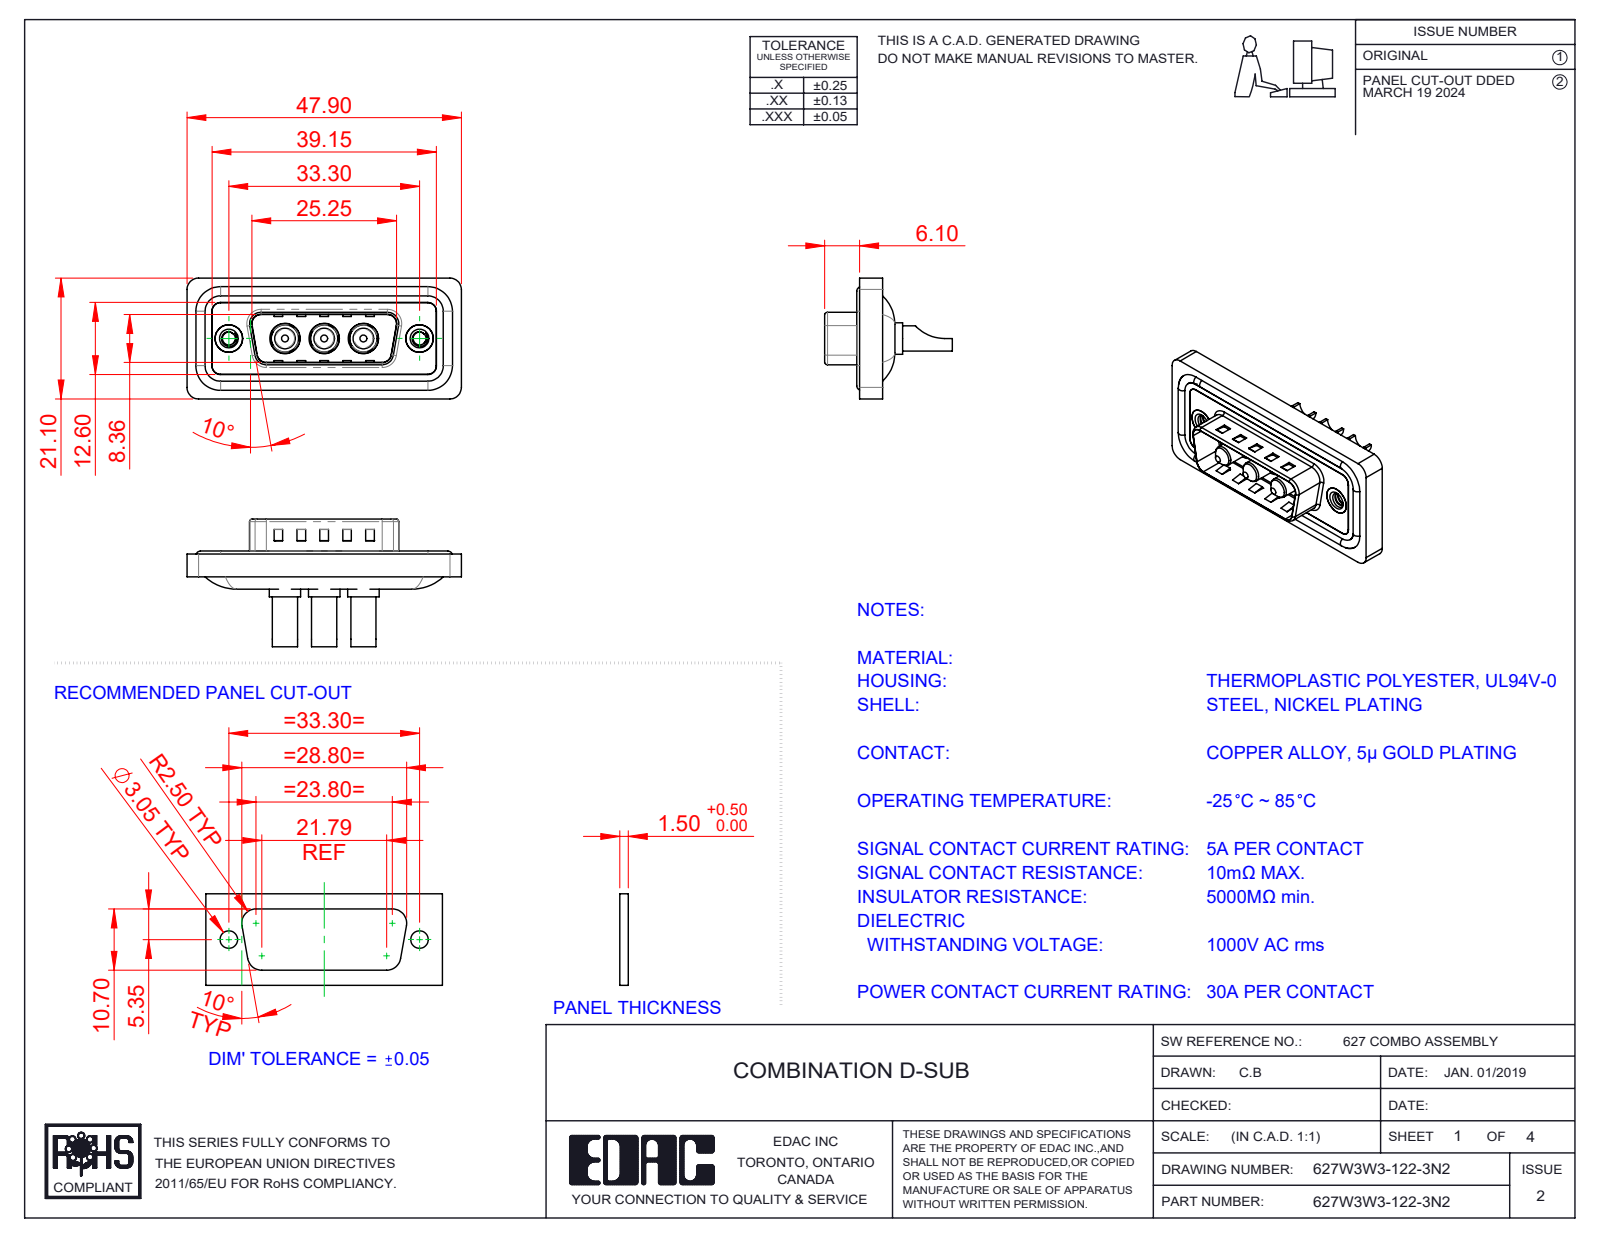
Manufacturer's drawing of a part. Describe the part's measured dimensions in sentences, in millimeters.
The part is named "627Combo Waterproof Housing_15 Contacts; Power Pin_30A SC; 627W3W3-122-3N2; 627Combo Shell Rear_15 Contacts (+3 more)". Its 3-D file was written by "SolidWorks 2023 (CONFIG_CONTROL_DESIGN)". It is 13 solids with 582 faces: 216 planar, 250 cylindrical and 116 other. Overall it measures 47.9 by 22.3 by 21.1 millimeters. Its volume is 5 658 cubic millimeters and its surface area 9 076 square millimeters. Round holes: 3 of diameter 3.5, 3 of diameter 4.85, 3 of diameter 5.3, 2 of diameter 2.26, 2 of diameter 4, 2 of diameter 4.8, 2 of diameter 5. Round bosses or shafts: 4 of diameter 1.6, 3 of diameter 5.5, 3 of diameter 5.2, 3 of diameter 4.75, 3 of diameter 4.4, 3 of diameter 3.75, 3 of diameter 3.6, 2 of diameter 4.9. Partial cylindrical surfaces (rounded edges, fillets, slot ends): 26 of radius 1.5, 20 of radius 2, 8 of radius 0.5, 8 of radius 1.6, 4 of radius 0.25, 4 of radius 0.6, 4 of radius 0.65, 4 of radius 0.9. The main face-to-face distances are 0.4, 1.1, 0.5, 1.6, 1.5, 3.1, 2.9, 0.82, 9.58, 2.5. The hole center spacings are 6.85, 9.8, 16.65, 23.5, 13.7, 33.3.
